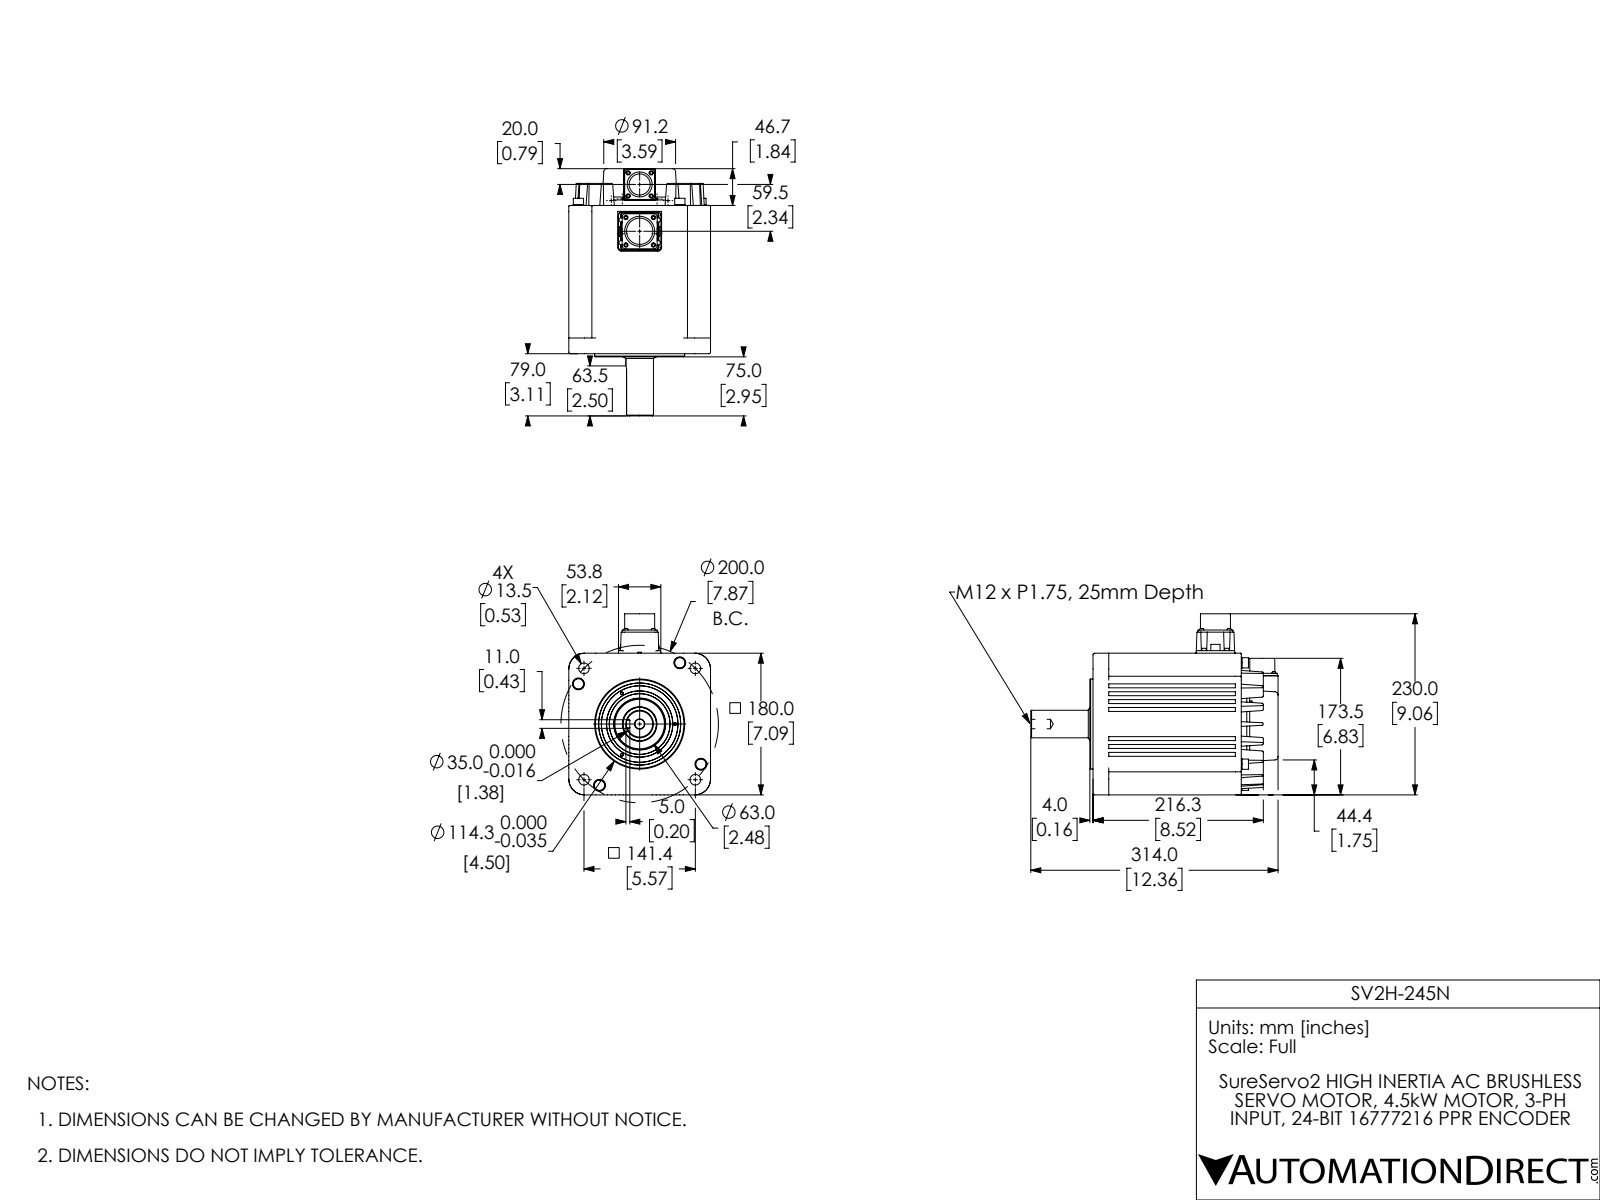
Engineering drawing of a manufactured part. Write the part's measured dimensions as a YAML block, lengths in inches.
part_name: "SV2H-x45N"
step_written_by: "SolidWorks 2017 (AUTOMOTIVE_DESIGN)"
units: inches
bodies: {solids: 1, faces: 628, planar: 319, cylindrical: 202, other: 107}
overall_size: [12.362, 9.056, 7.087]
volume: 365.7
surface_area: 489
round_holes:
  - {diameter: 0.531, count: 4}
  - {diameter: 0.472, count: 1}
  - {diameter: 1.058, count: 1}
  - {diameter: 1.317, count: 1}
  - {diameter: 2.48, count: 1}
round_bosses_or_shafts:
  - {diameter: 0.217, count: 7}
  - {diameter: 0.528, count: 4}
  - {diameter: 0.512, count: 4}
  - {diameter: 0.315, count: 4}
  - {diameter: 4.567, count: 1}
  - {diameter: 4.5, count: 1}
  - {diameter: 1.732, count: 1}
  - {diameter: 1.673, count: 1}
partial_cylinders:
  - {radius: 0.197, count: 17}
  - {radius: 0.064, count: 16}
  - {radius: 0.157, count: 16}
  - {radius: 0.039, count: 12}
  - {radius: 0.02, count: 8}
  - {radius: 0.079, count: 4}
  - {radius: 0.394, count: 4}
  - {radius: 0.787, count: 4}
face_to_face_distances: [0.197, 7.087, 0.394, 1.154, 5.933, 0.591, 3.031, 7.413, 3.228, 2.835]
hole_center_spacings: [3.937, 5.568, 7.874, 2.343]
